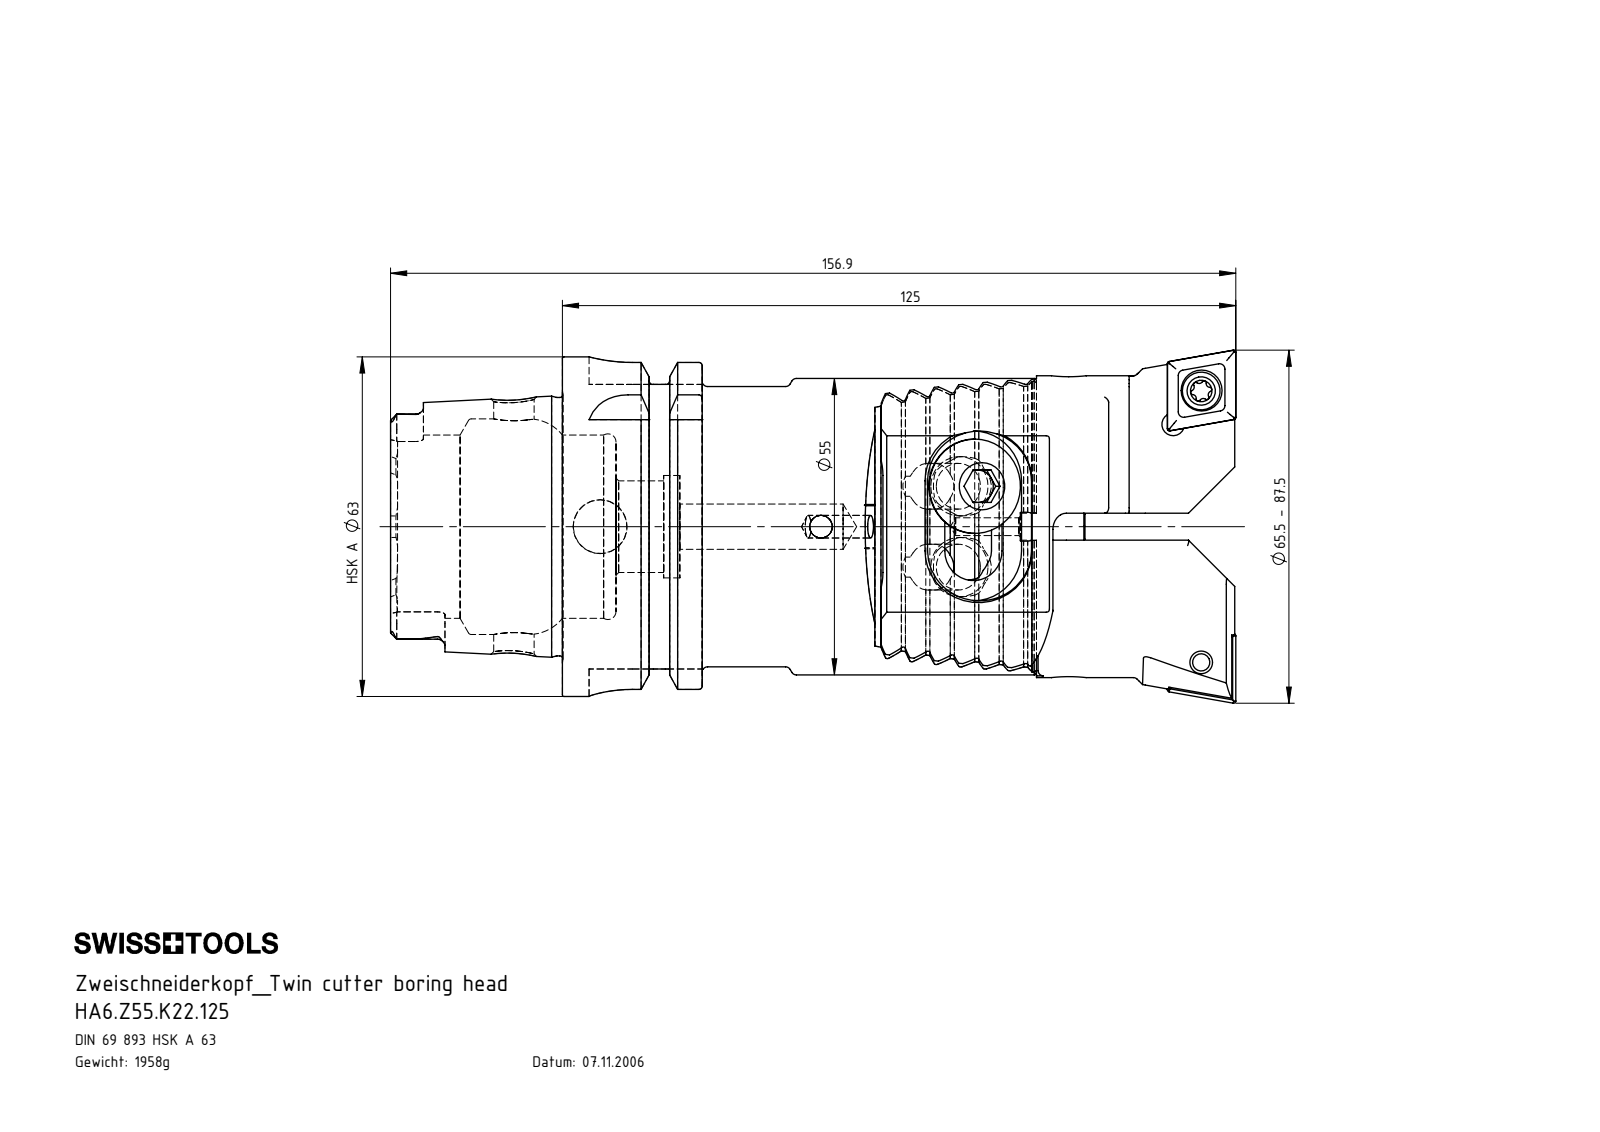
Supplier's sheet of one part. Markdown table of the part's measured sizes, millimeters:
| quantity | value |
| --- | --- |
| part name | Z55-xxx.001.037_C; Z55-ER1.001.025; HA6-Z55.K21.125_A_Fertigbearbeitung; CCMT120404 (+6 more) |
| STEP written by | SolidWorks 2022 (CONFIG_CONTROL_DESIGN) |
| units | millimeters |
| bodies | 13 solids, 858 faces (346 planar, 249 cylindrical, 263 other) |
| overall size | 156.9 × 65.5 × 63 |
| volume | 250 022 mm³ |
| surface area | 62 414 mm² |
| round holes (diameter × count) | 4.2 × 7, 2 × 2, 5.5 × 2, 7.6 × 2, 8.5 × 2, 10.5 × 2, 11 × 2, 3.3 × 1, 5 × 1, 7.5 × 1, 8.4 × 1, 10 × 1 |
| round bosses / shafts (diameter × count) | 17.5 × 2, 17 × 2, 10 × 2, 7 × 2, 5 × 2, 63 × 1, 55 × 1, 54.95 × 1 |
| partial cylindrical surfaces (radius × count) | 0.34 × 14, 1 × 14, 0.34 × 12, 0.39 × 12, 0.69 × 12, 1.4 × 6, 3 × 6, 2.88 × 4 |
| main face-to-face distances | 4.07, 8.14, 12.21, 16.28, 4.11, 20.35, 4.03, 4.01, 8.18, 4.13 |
| hole center spacings | 8.08, 8.2, 16, 44.46, 44.55, 50.43, 68.08, 74.93 |
